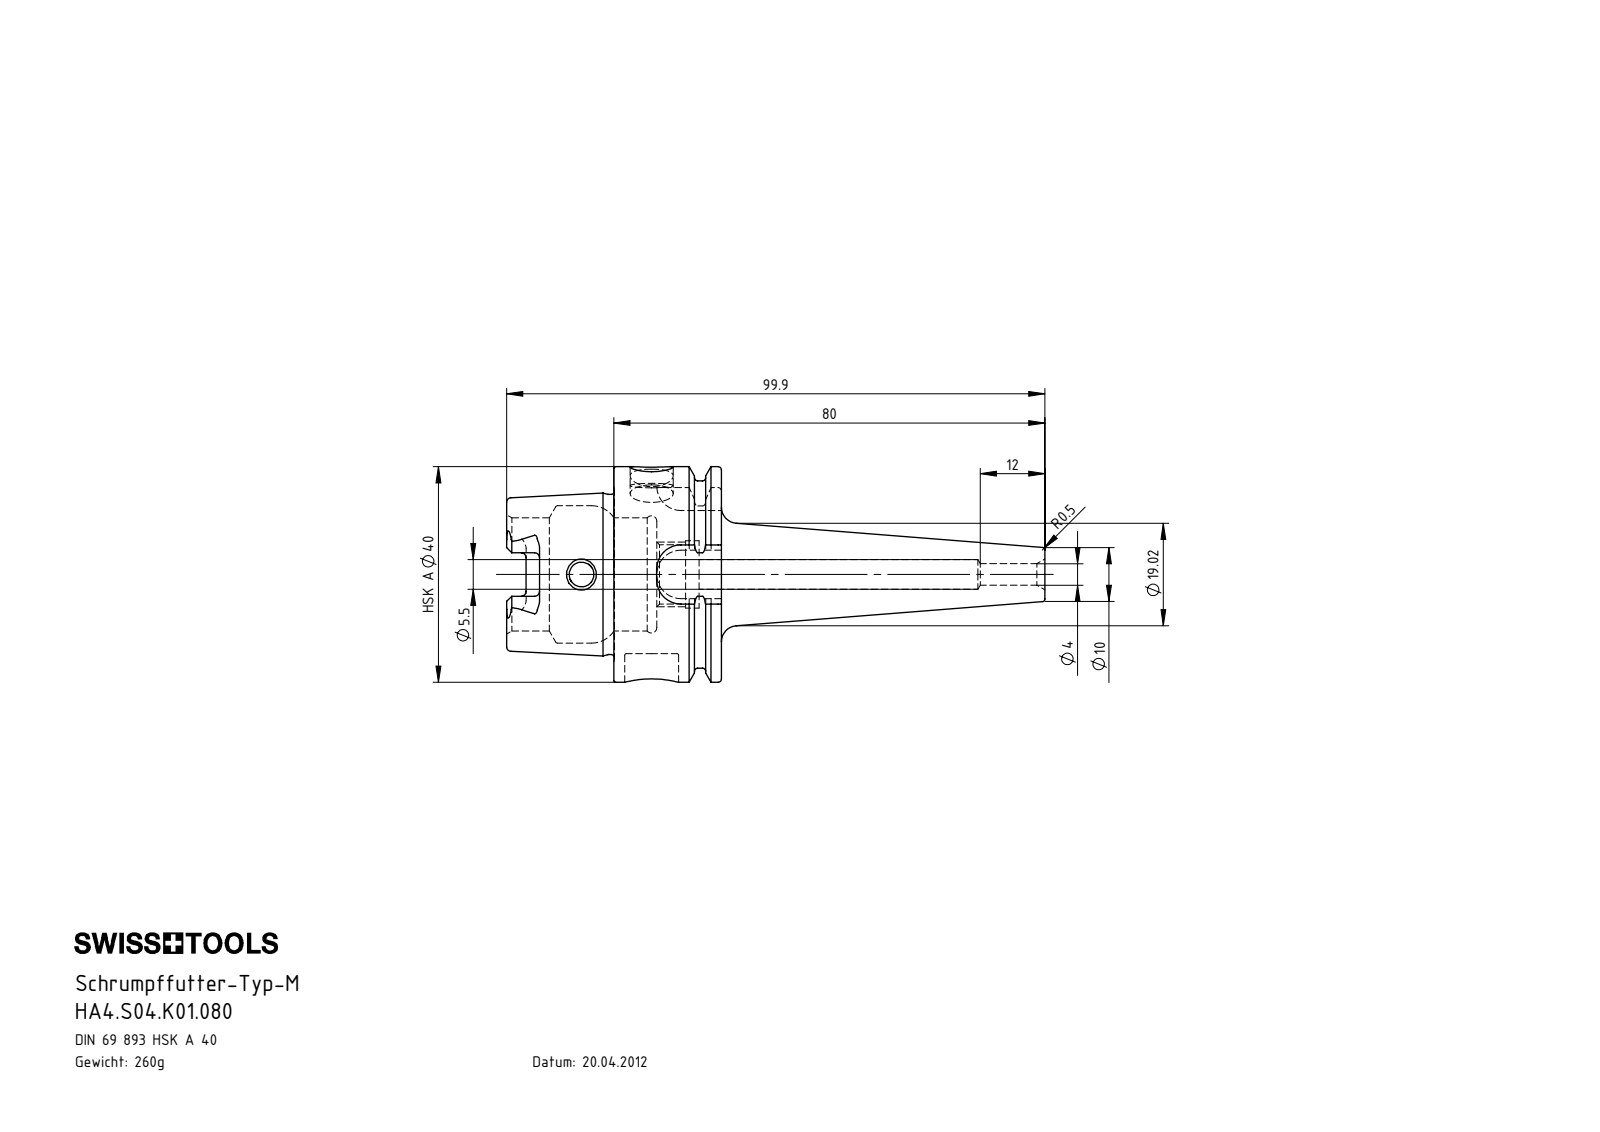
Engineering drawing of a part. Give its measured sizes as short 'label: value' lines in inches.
name: HA4-S04.K01.080_A_Fertigbearbeitung; HA4.S04.K01.080
written by: SolidWorks 2017 (AUTOMOTIVE_DESIGN)
unit: in
bodies: 1 solid, 165 faces (46 planar, 50 cylindrical, 69 other)
size: 3.933 × 1.575 × 1.575
volume: 2.018 in³; area: 20.48 in²
holes: 2× ⌀0.315, 1× ⌀0.157, 1× ⌀0.181, 1× ⌀0.217, 1× ⌀0.394, 1× ⌀0.433, 1× ⌀0.492, 1× ⌀0.827, 1× ⌀1.004
bosses: 1× ⌀1.575, 1× ⌀1.368, 1× ⌀1.17
rounds: 6× R0.035, 4× R0.074, 4× R0.177
face distances: 0.785, 0.313, 0.472, 0.783, 1.096, 1.569, 1.406, 0.622, 0.309, 0.163
